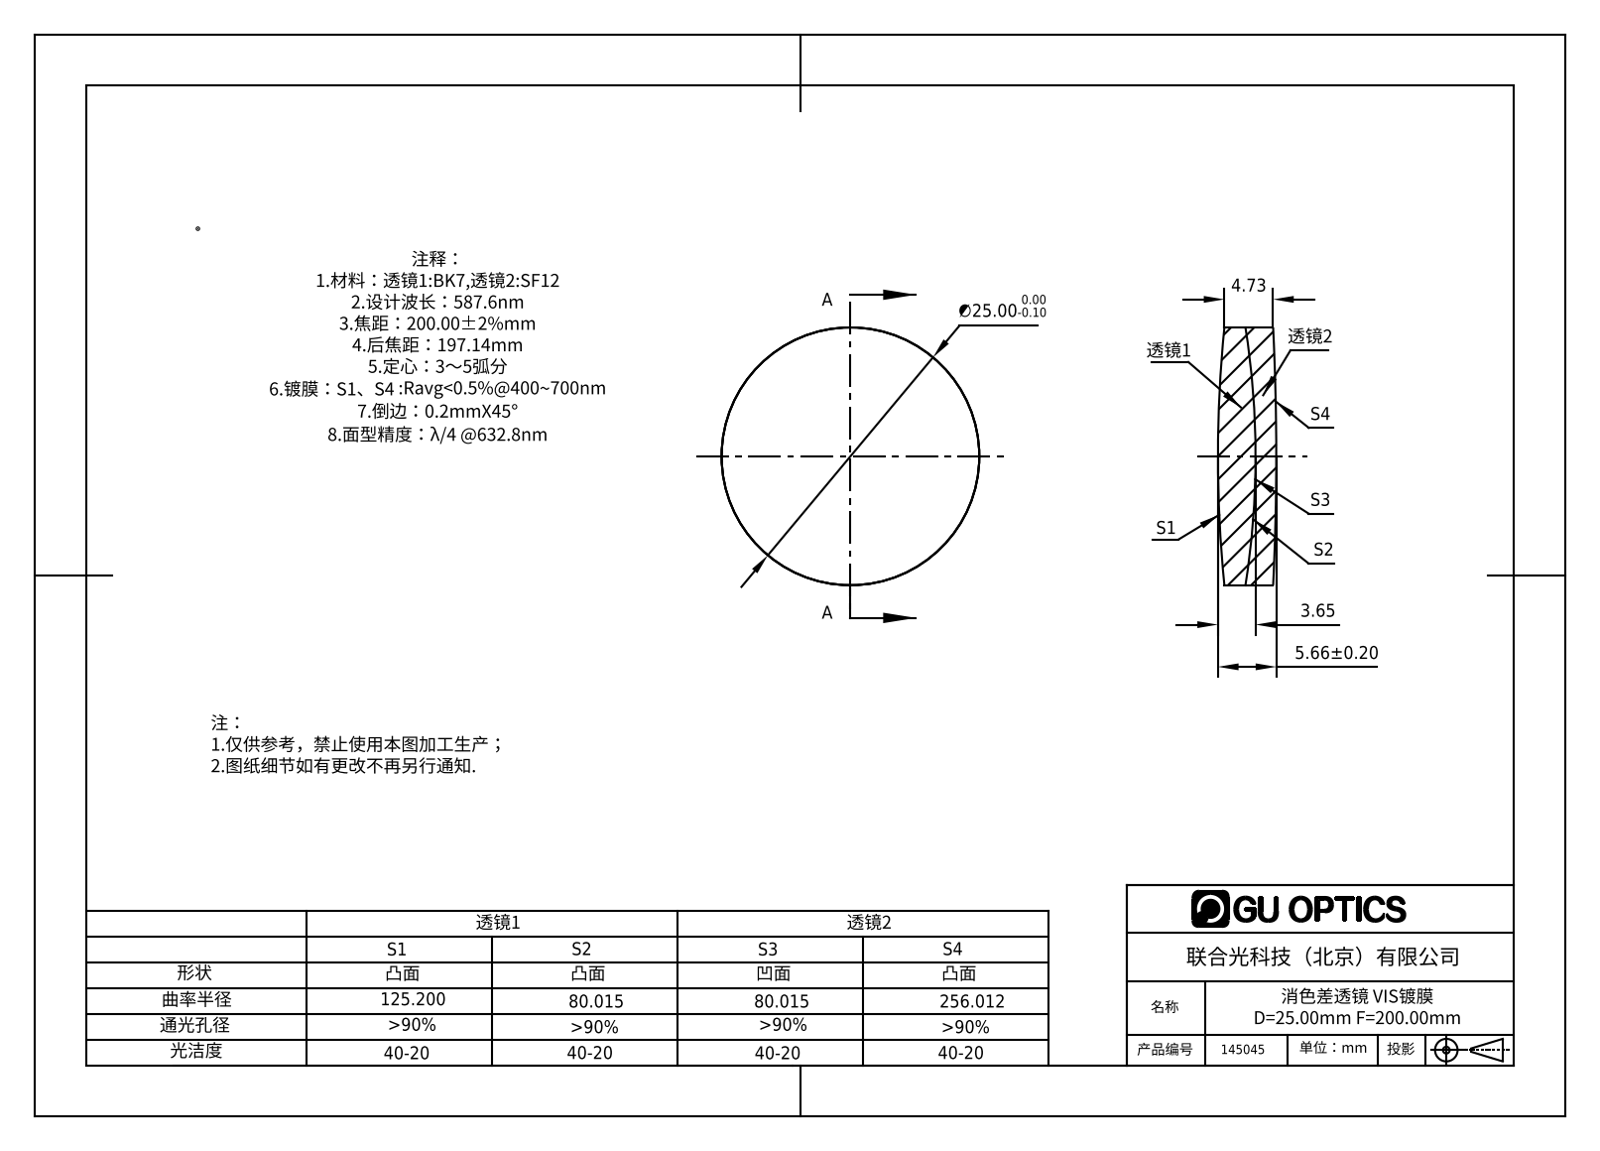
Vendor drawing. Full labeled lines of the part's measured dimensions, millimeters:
Part name (STEP PRODUCT): 145045
STEP written by: SolidWorks 2016 (AUTOMOTIVE_DESIGN)
Units: millimetres
Bodies: 2 solids, 12 faces (0 planar, 4 cylindrical, 8 other)
Overall size (bounding box): 25 × 25 × 5.66
Volume: 2 550 mm³ · Surface area: 2 342 mm²
Round bosses / shafts (diameter × count): ⌀25 ×1
